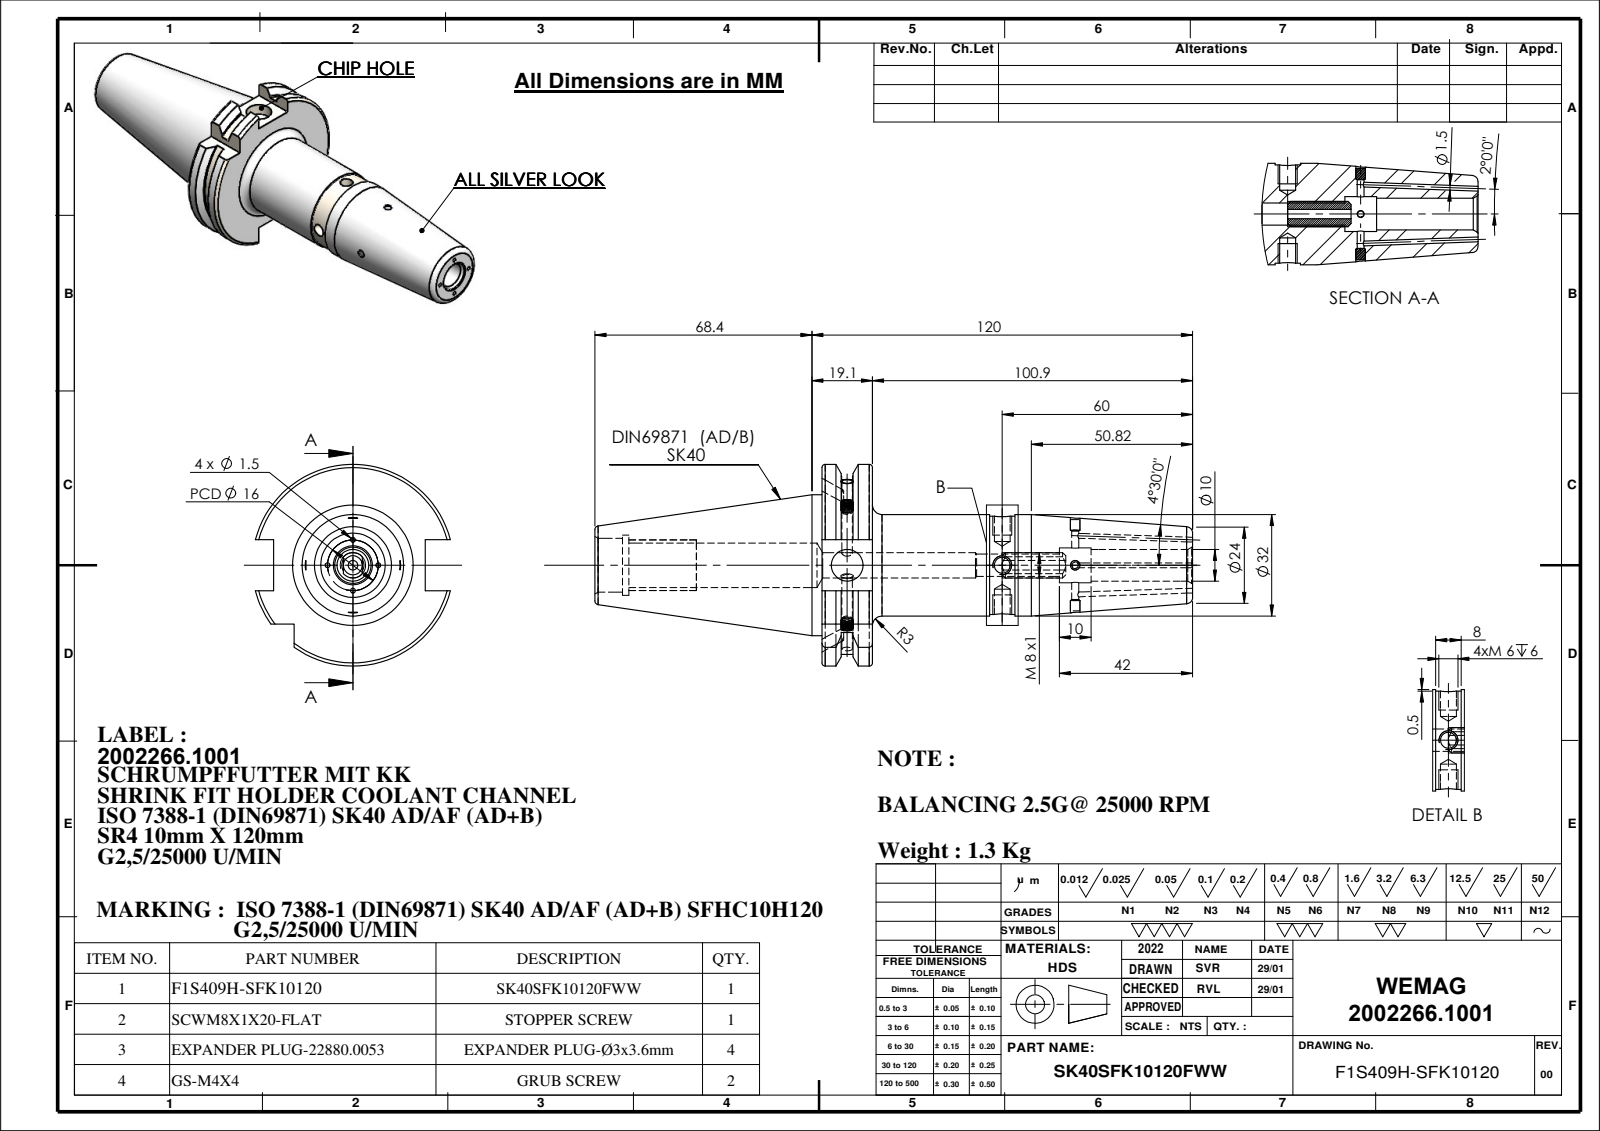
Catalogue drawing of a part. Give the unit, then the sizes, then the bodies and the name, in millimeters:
Units: millimetres
Overall size (bounding box): 188.4 × 63.55 × 61.48
Round holes (diameter × count): ⌀1.5 ×4, ⌀3 ×3, ⌀2.2 ×2, ⌀5 ×2, ⌀3.3 ×1, ⌀7 ×1, ⌀9.99 ×1, ⌀10 ×1, ⌀10.99 ×1, ⌀14 ×1, ⌀17 ×1, ⌀19 ×1
Round bosses / shafts (diameter × count): ⌀4 ×2, ⌀44.45 ×1, ⌀32 ×1, ⌀31 ×1, ⌀8 ×1
Partial cylindrical surfaces — rounded edges, fillets, slot ends (radius × count): R28.12 ×1, R31.77 ×1
Main face-to-face distances: 15.9, 116.8, 100.9, 16.1, 47.8, 22, 60.9, 76.8, 71.6, 87.5
Hole centre spacings: 23, 48.85, 71.85
Volume: 165 148 mm³ · Surface area: 35 550 mm²
Bodies: 8 solids, 293 faces (62 planar, 105 cylindrical, 126 other)
Part name (STEP PRODUCT): EXPANDER PLUG Ø3x3.6; 91406-SR410120; GS-M4X4_DIN 913 - M4 x 4-N; SK40SFK10120FWW (+1 more)
STEP written by: SolidWorks 2018 (CONFIG_CONTROL_DESIGN)
